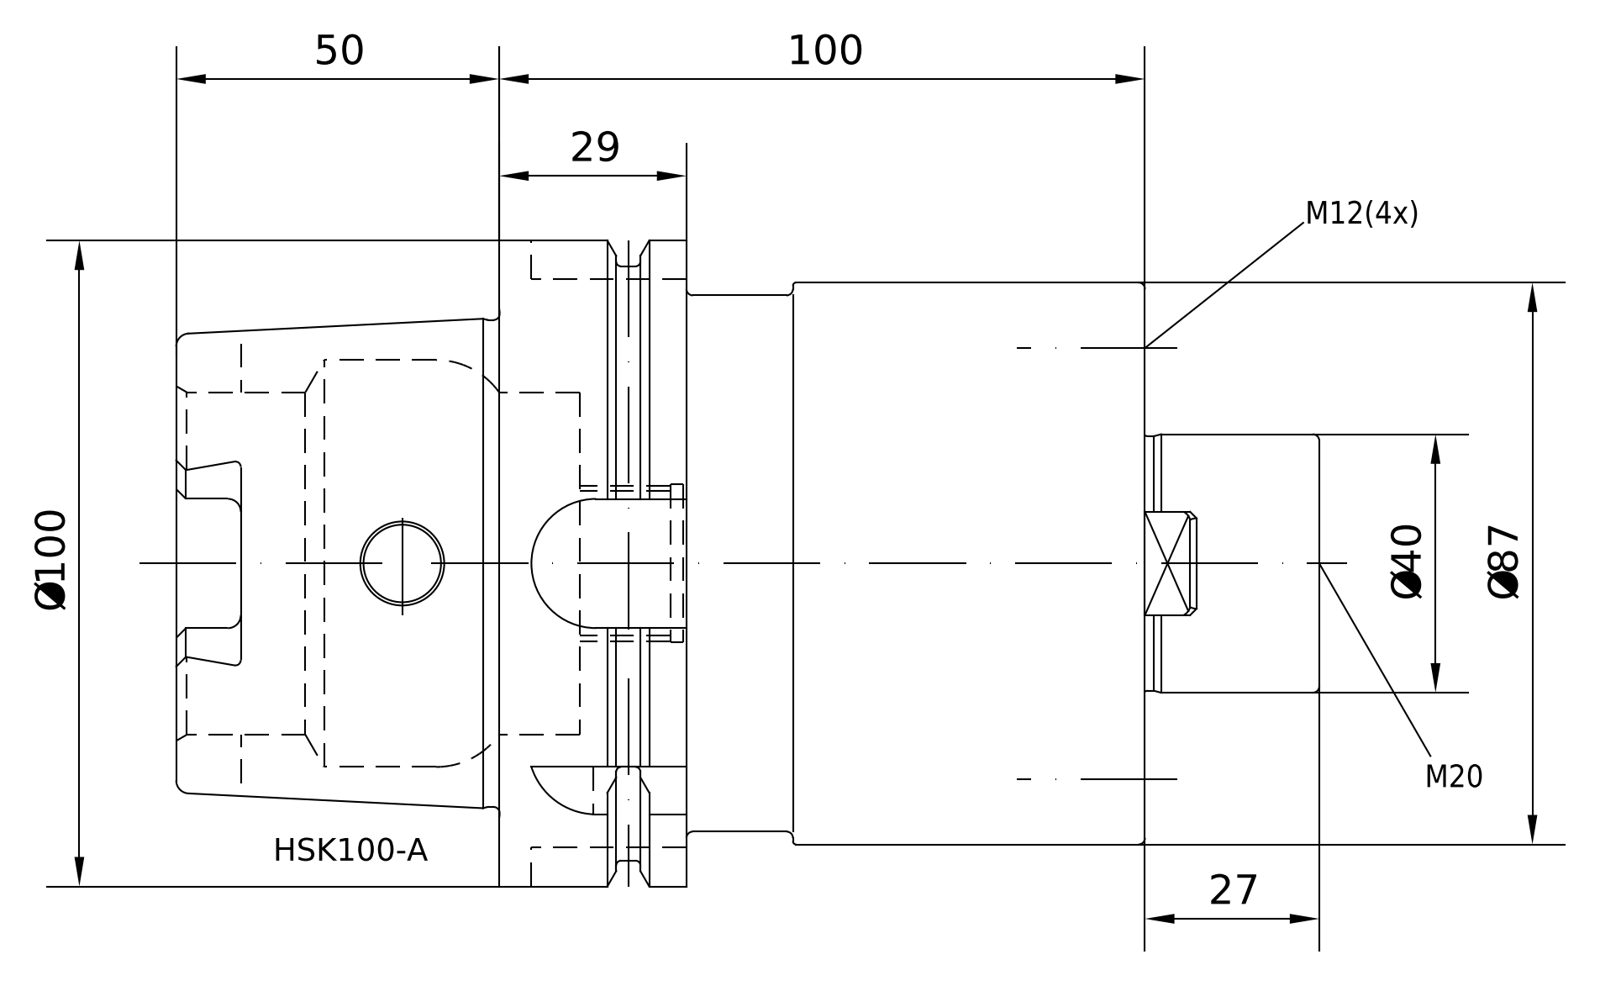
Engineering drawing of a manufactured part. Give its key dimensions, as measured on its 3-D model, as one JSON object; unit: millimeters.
{"part_name": "A100-051-40", "step_written_by": "PRO/ENGINEER BY PARAMETRIC TECHNOLOGY CORPORATION, 2010430 (CONFIG_CONTROL_DESIGN)", "units": "millimeters", "bodies": {"solids": 1, "faces": 226, "planar": 66, "cylindrical": 73, "other": 87}, "overall_size": [177, 100, 100], "volume_mm3": 685758, "surface_area_mm2": 85590, "round_holes": [[12, 5], [10.2, 4], [10, 1], [17.5, 1], [20, 1], [22.5, 1], [24, 1], [24.32, 1], [24.5, 1], [53, 1], [63, 1]], "round_bosses_or_shafts": [[100, 1], [92, 1], [87, 1], [83, 1], [75.36, 1], [40, 1]], "partial_cylinders_radius": [[2, 6], [5, 4], [8, 1], [10, 1], [11, 1]], "face_to_face_distances": [100, 71, 29, 12.5, 16.5, 79, 87.5, 62.5, 16, 127], "hole_center_spacings": [33.35, 47.16, 66.69]}
